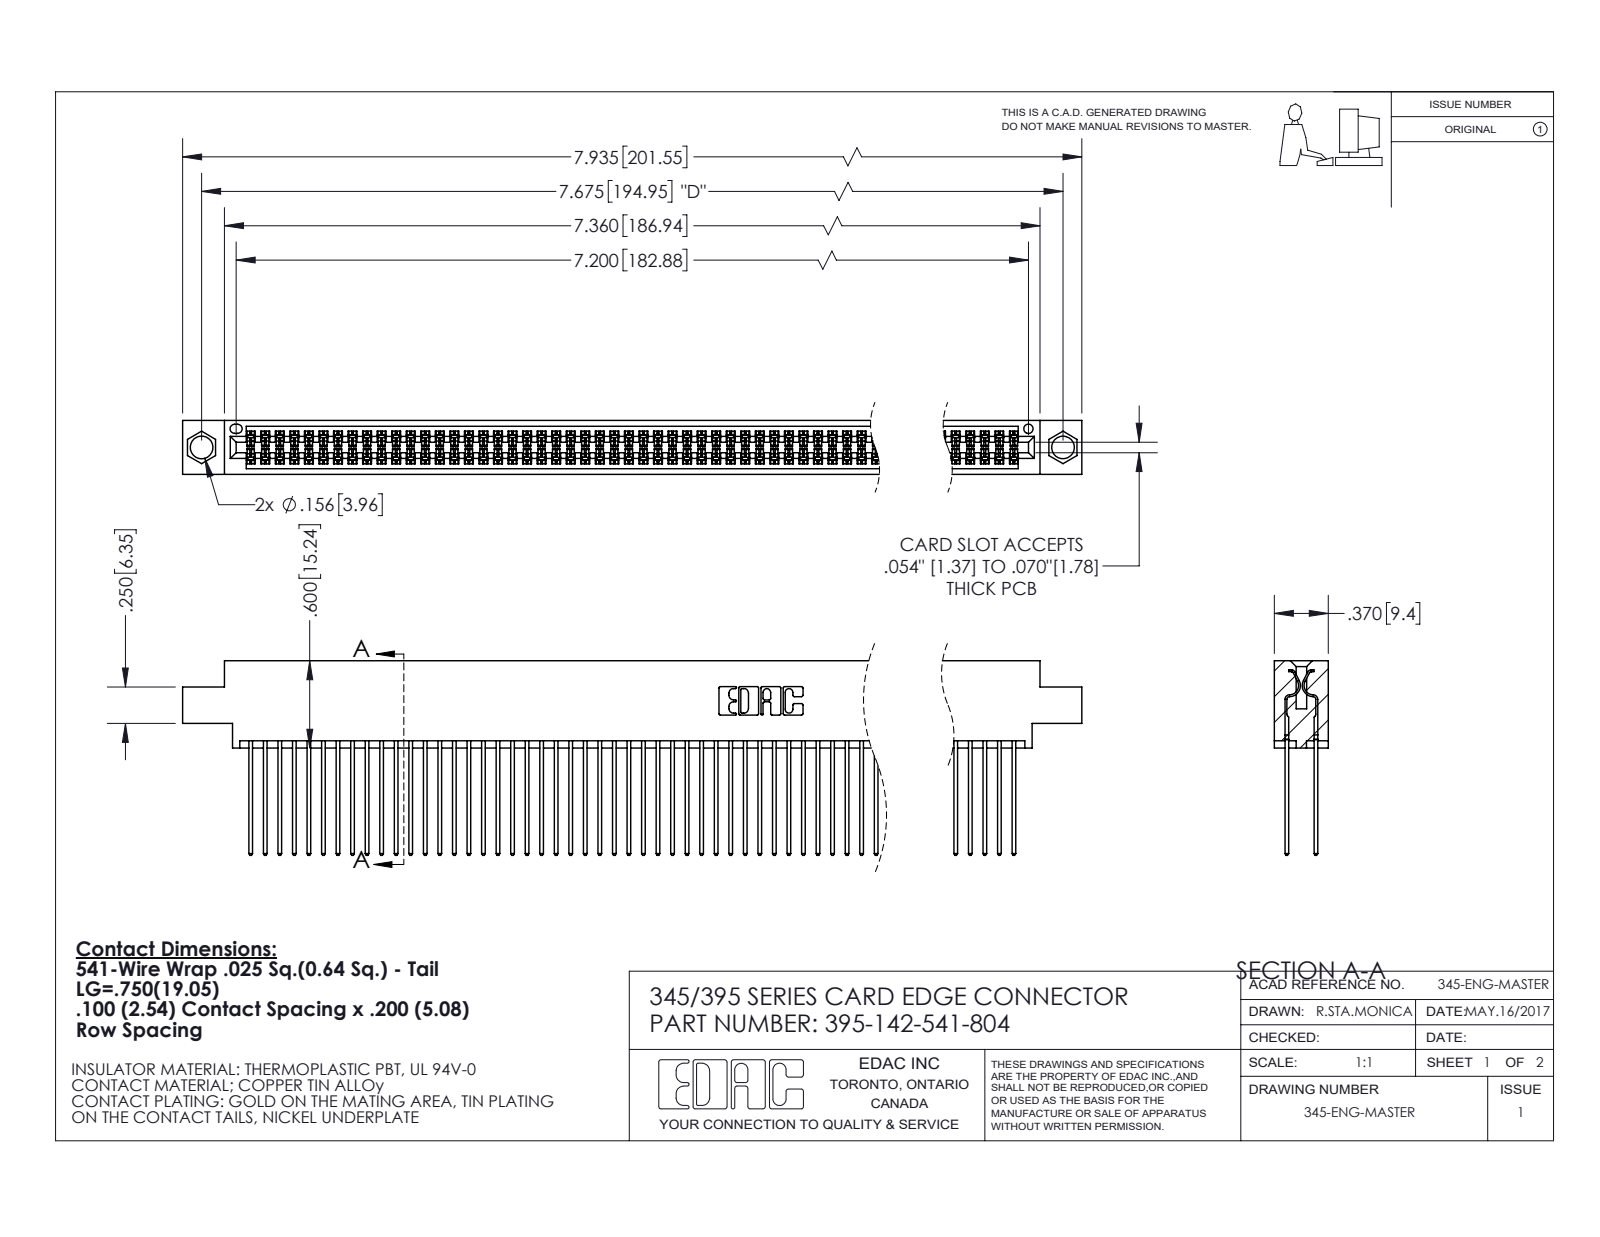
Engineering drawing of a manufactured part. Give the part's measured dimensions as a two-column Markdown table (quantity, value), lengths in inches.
| quantity | value |
| --- | --- |
| part name | 395-142-541-804; 345 Part_0.170 Offset - 0.156 Dia-TI; 345-292-001_345-293-141 |
| STEP written by | SolidWorks 2020 (CONFIG_CONTROL_DESIGN) |
| units | inches |
| bodies | 143 solids, 7244 faces (4784 planar, 2460 cylindrical, 0 other) |
| overall size | 7.935 × 1.337 × 0.37 |
| volume | 1.248 in³ |
| surface area | 53.64 in² |
| round holes (diameter × count) | 0.156 × 2, 0.064 × 1 |
| partial cylindrical surfaces (radius × count) | 0.006 × 213, 0.01 × 142, 0.01 × 22, 0.007 × 6, 0.031 × 6, 0.026 × 3, 0.014 × 2, 0.019 × 2 |
| main face-to-face distances | 0.072, 0.298, 0.2, 0.098, 0.272, 0.025, 0.225, 0.37, 0.175, 0.149 |
| hole center spacings | 0.27, 7.439, 7.675 |
